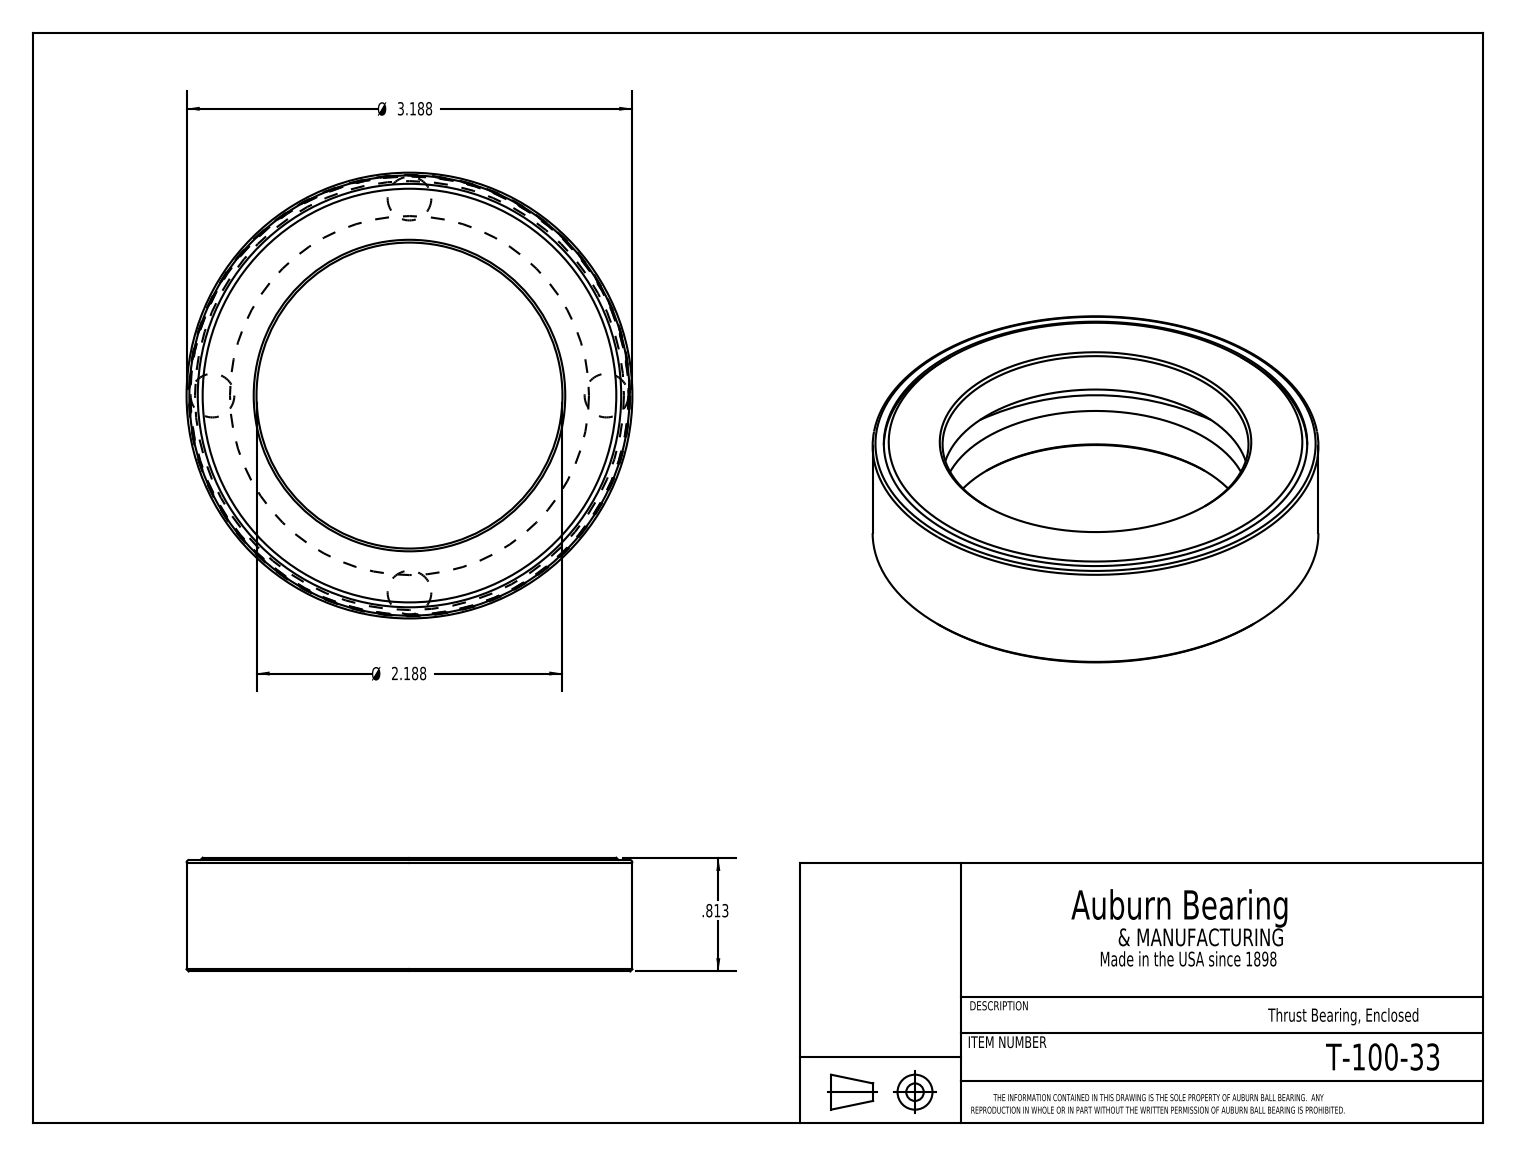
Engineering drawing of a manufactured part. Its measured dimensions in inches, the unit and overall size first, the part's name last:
Units: inches
Overall size (bounding box): 3.188 × 3.188 × 0.813
Round holes (diameter × count): ⌀2.187 ×1, ⌀3.027 ×1, ⌀3.147 ×1
Round bosses / shafts (diameter × count): ⌀3.187 ×1, ⌀3.133 ×1
Main face-to-face distances: 0.313, 0.5, 0.813, 0.187, 0.778, 0.465, 0.278, 0.035, 0.798, 0.485
Volume: 2.491 in³ · Surface area: 38.81 in²
Bodies: 6 solids, 28 faces (9 planar, 7 cylindrical, 12 other)
Part name (STEP PRODUCT): T-100-33
STEP written by: SolidWorks 2016 (CONFIG_CONTROL_DESIGN)
